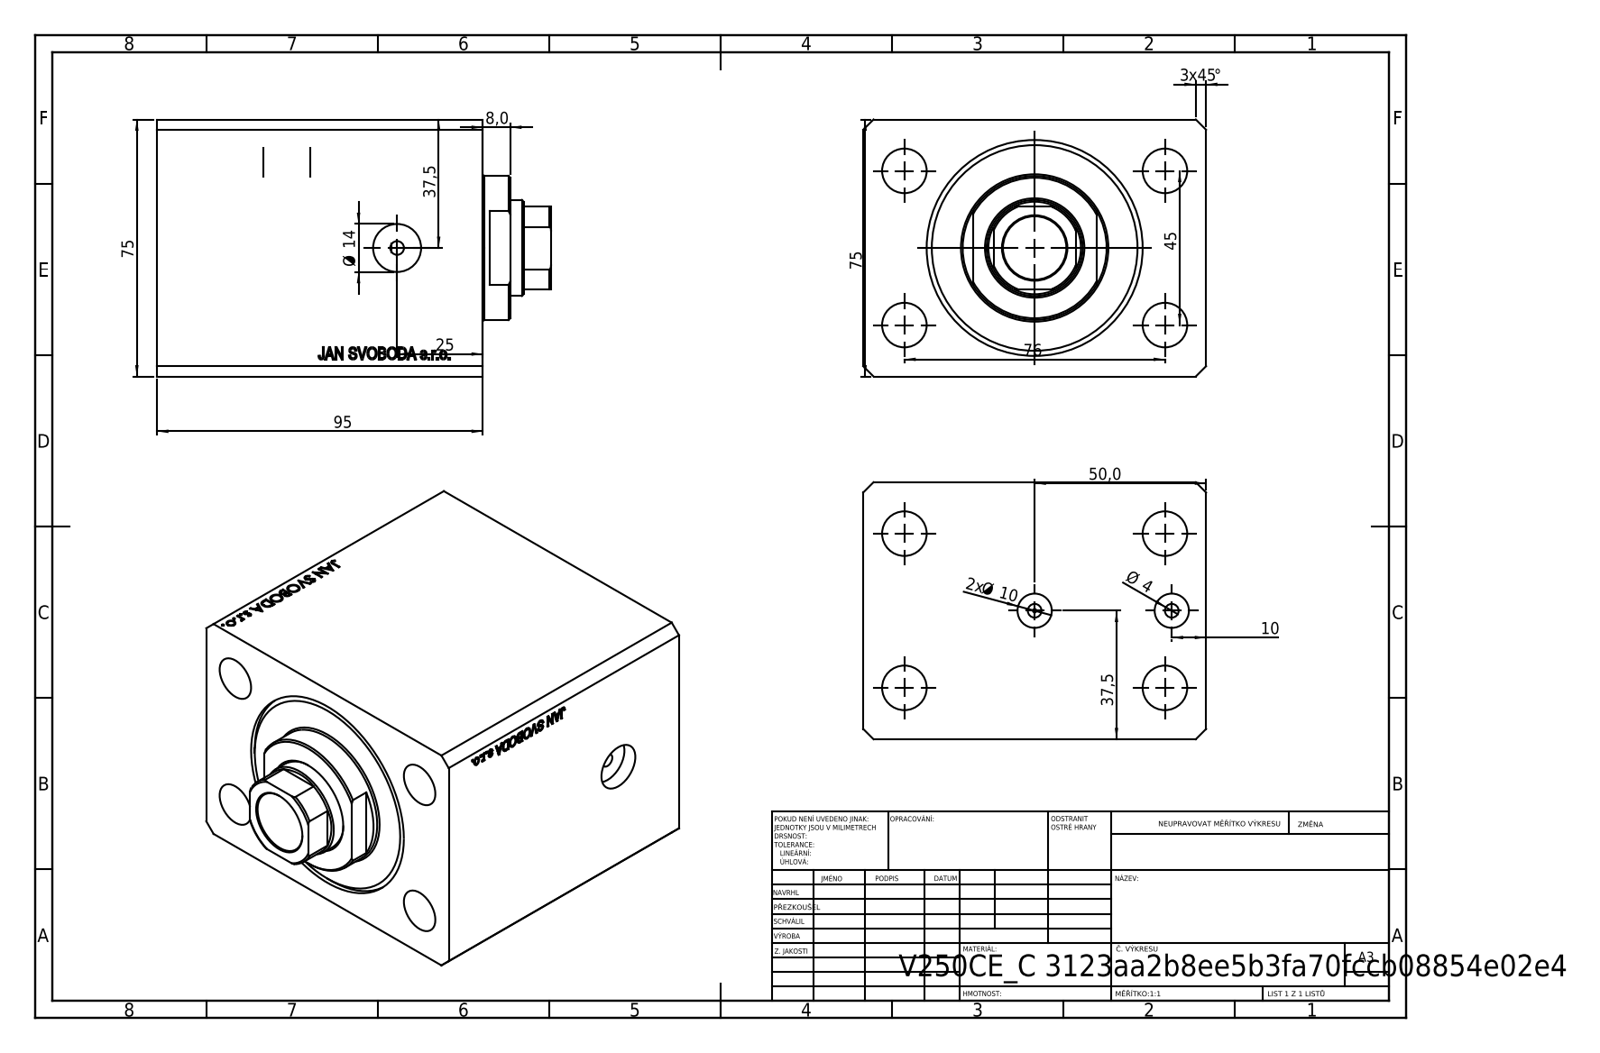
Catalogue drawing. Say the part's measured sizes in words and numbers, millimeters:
The part is named "V250CE_C_VCP; V250CE_VC_C; V250CE_C_Body". Its 3-D file was written by "SolidWorks 2019 (CONFIG_CONTROL_DESIGN)". It is 3 solids with 868 faces: 428 planar, 46 cylindrical and 394 other. Overall it measures 114.9 by 100 by 75 millimeters. Its volume is 637 321 cubic millimeters and its surface area 110 346 square millimeters. Round holes: 4 of diameter 4, 4 of diameter 13, 2 of diameter 10, 2 of diameter 14, 1 of diameter 1.25, 1 of diameter 18.5, 1 of diameter 28, 1 of diameter 50, 1 of diameter 63. Round bosses or shafts: 1 of diameter 42. Partial cylindrical surfaces (rounded edges, fillets, slot ends): 1 of radius 13.5. The main face-to-face distances are 75, 100, 95, 11.9, 83.1, 68.4, 56.5, 26.6, 20, 48.4. The hole center spacings are 44.16, 45, 22.59, 76, 81.18, 88.32, 40.
